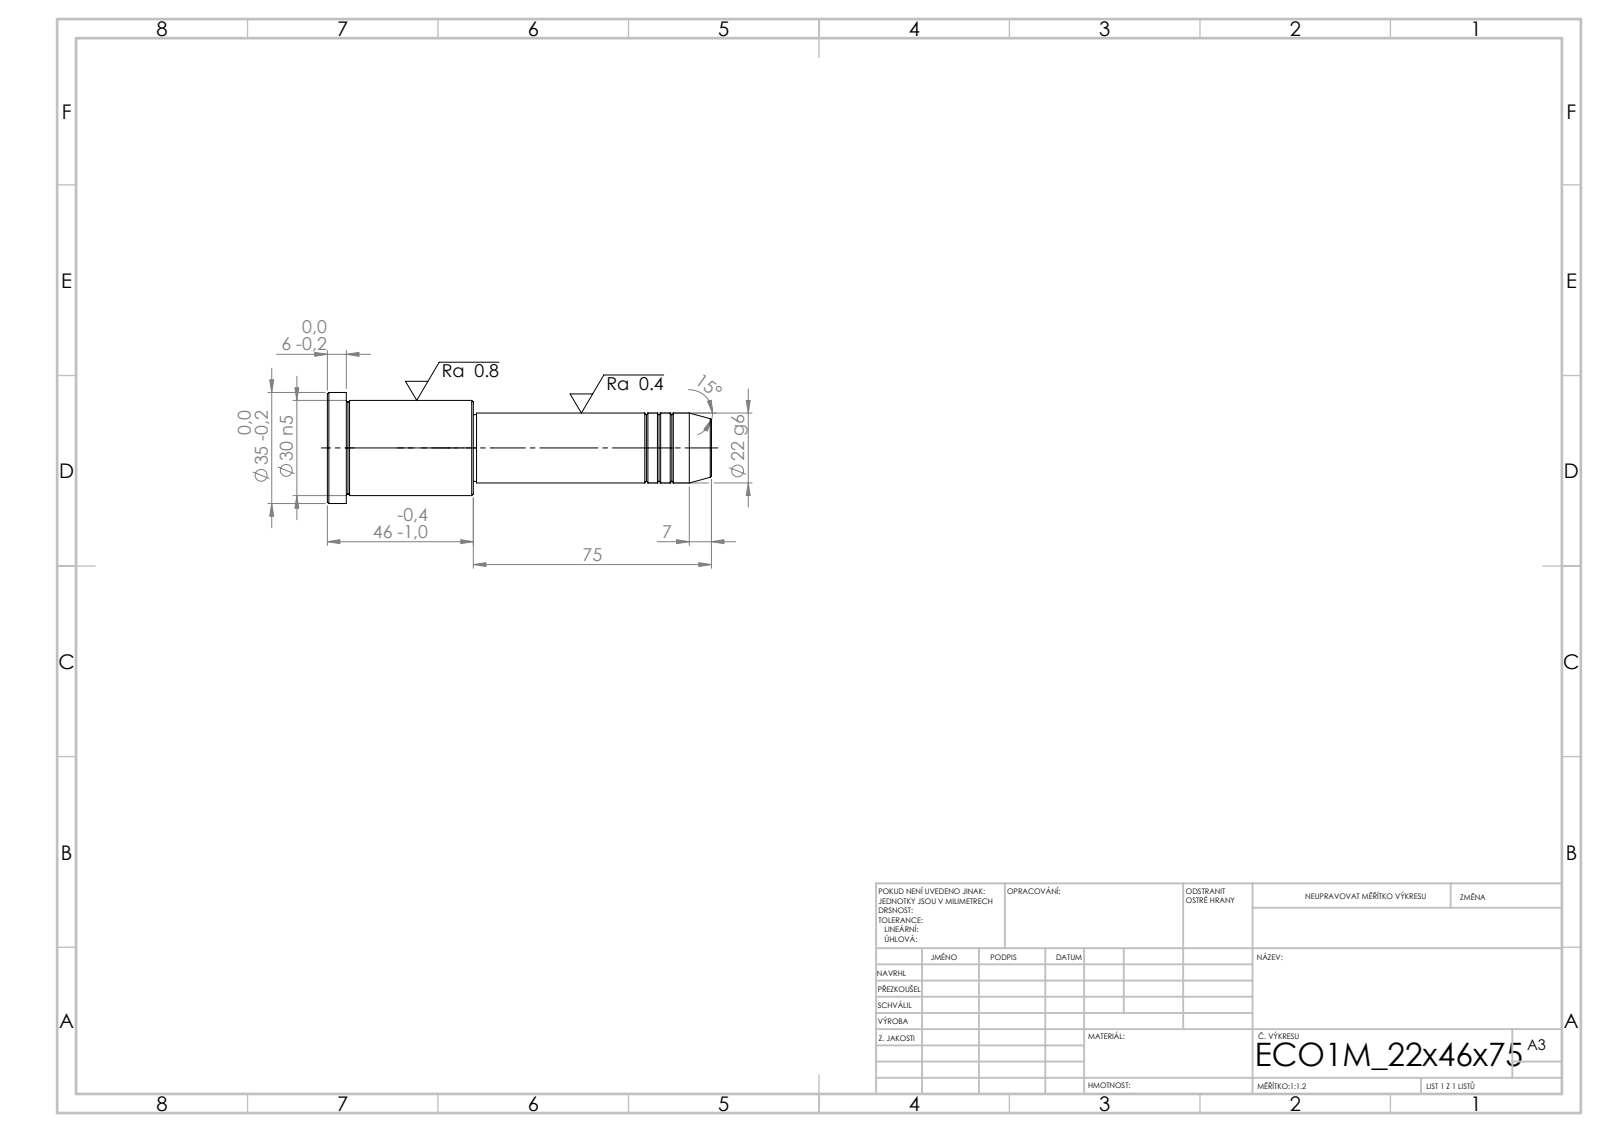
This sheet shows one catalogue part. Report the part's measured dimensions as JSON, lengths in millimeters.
{"step_written_by": "SolidWorks 2019 (CONFIG_CONTROL_DESIGN)", "units": "millimeters", "bodies": {"solids": 1, "faces": 43, "planar": 5, "cylindrical": 14, "other": 24}, "overall_size": [121, 35, 35], "volume_mm3": 61952, "surface_area_mm2": 11550, "round_bosses_or_shafts": [[35, 1], [30, 1], [22, 1], [21, 1]], "face_to_face_distances": [46, 40, 6, 75, 115, 121, 74, 1, 41, 47]}
